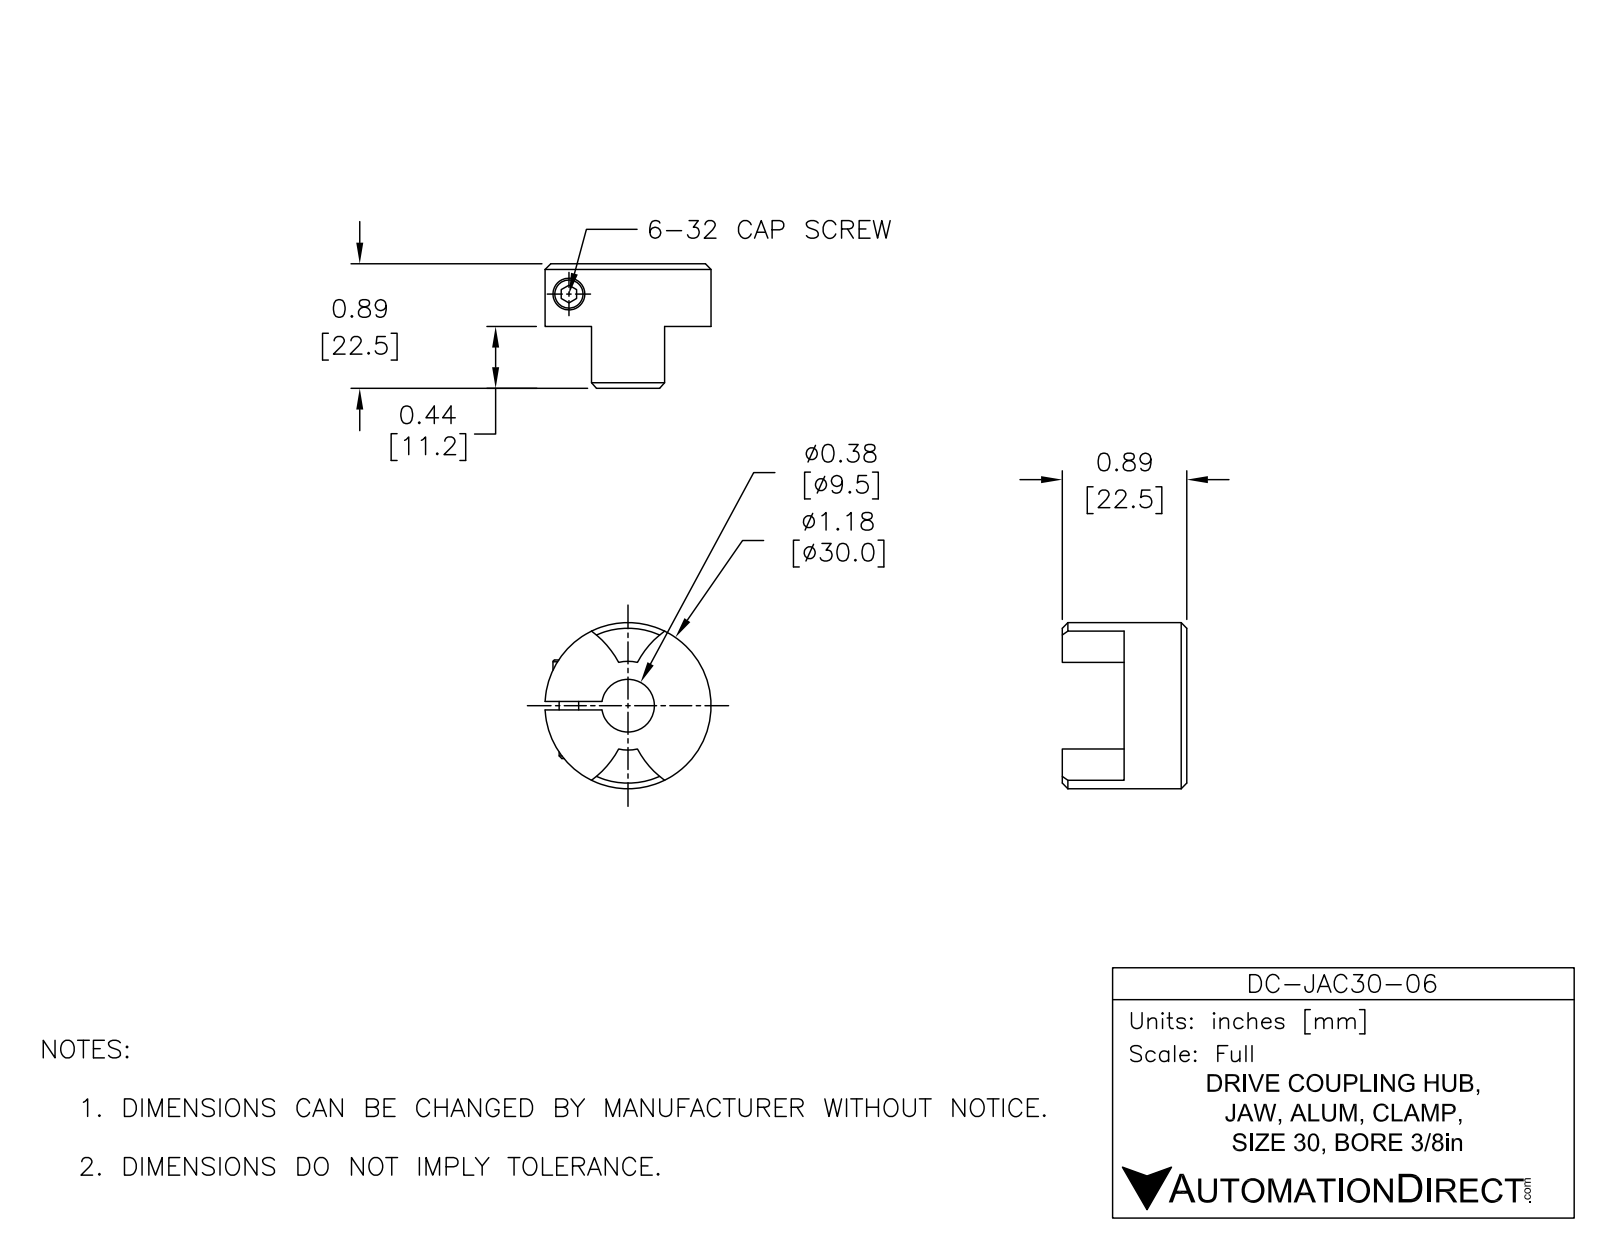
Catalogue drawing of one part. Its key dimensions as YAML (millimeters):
part_name: "DC-JAC30-06"
step_written_by: "SolidWorks 2015 (AUTOMOTIVE_DESIGN)"
units: millimeters
bodies: {solids: 1, faces: 27, planar: 7, cylindrical: 16, other: 4}
overall_size: [29.97, 29.95, 22.48]
volume: 7839
surface_area: 3680
round_holes:
  - {diameter: 3.91, count: 1}
  - {diameter: 6.35, count: 1}
  - {diameter: 9.53, count: 1}
round_bosses_or_shafts:
  - {diameter: 29.97, count: 1}
partial_cylinders:
  - {radius: 16.64, count: 2}
  - {radius: 8, count: 1}
face_to_face_distances: [11.3, 1.52, 22.48, 11.18, 5.51, 3.99]
